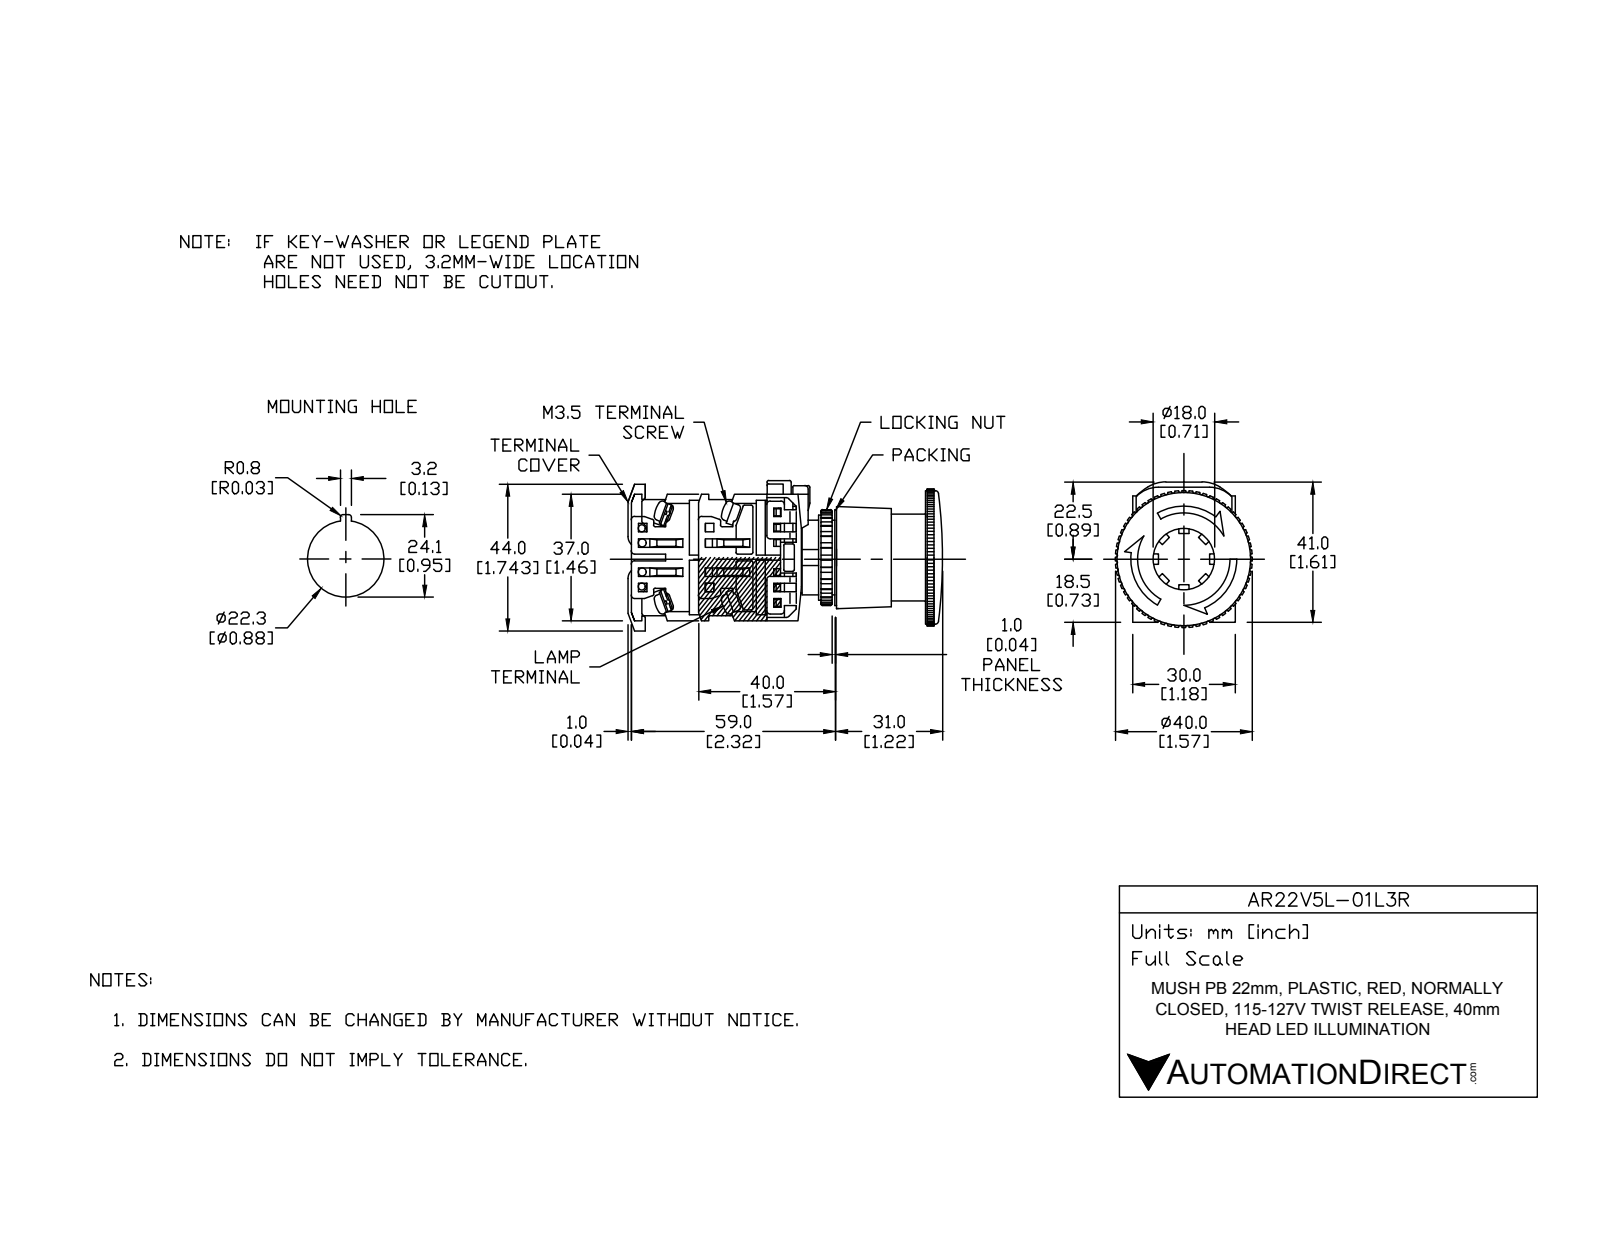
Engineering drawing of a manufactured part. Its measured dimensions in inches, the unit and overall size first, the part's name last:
Units: inches
Overall size (bounding box): 3.642 × 1.725 × 1.574
Round holes (diameter × count): ⌀0.858 ×1, ⌀0.866 ×1, ⌀1 ×1
Round bosses / shafts (diameter × count): ⌀0.197 ×4, ⌀1.173 ×1, ⌀0.984 ×1, ⌀0.945 ×1, ⌀0.856 ×1, ⌀0.669 ×1
Partial cylindrical surfaces — rounded edges, fillets, slot ends (radius × count): R0.02 ×119, R0.069 ×8, R0.197 ×4, R0.157 ×2, R0.531 ×1, R0.591 ×1, R0.653 ×1, R0.693 ×1
Main face-to-face distances: 0.039, 0.709, 1.142, 0.787, 0.394, 0.079, 0.63, 0.748, 0.807, 0.014
Volume: 3.43 in³ · Surface area: 43.81 in²
Bodies: 17 solids, 725 faces (308 planar, 310 cylindrical, 107 other)
Part name (STEP PRODUCT): AR22V5L-01L3R
STEP written by: SolidWorks 2017 (AUTOMOTIVE_DESIGN)
